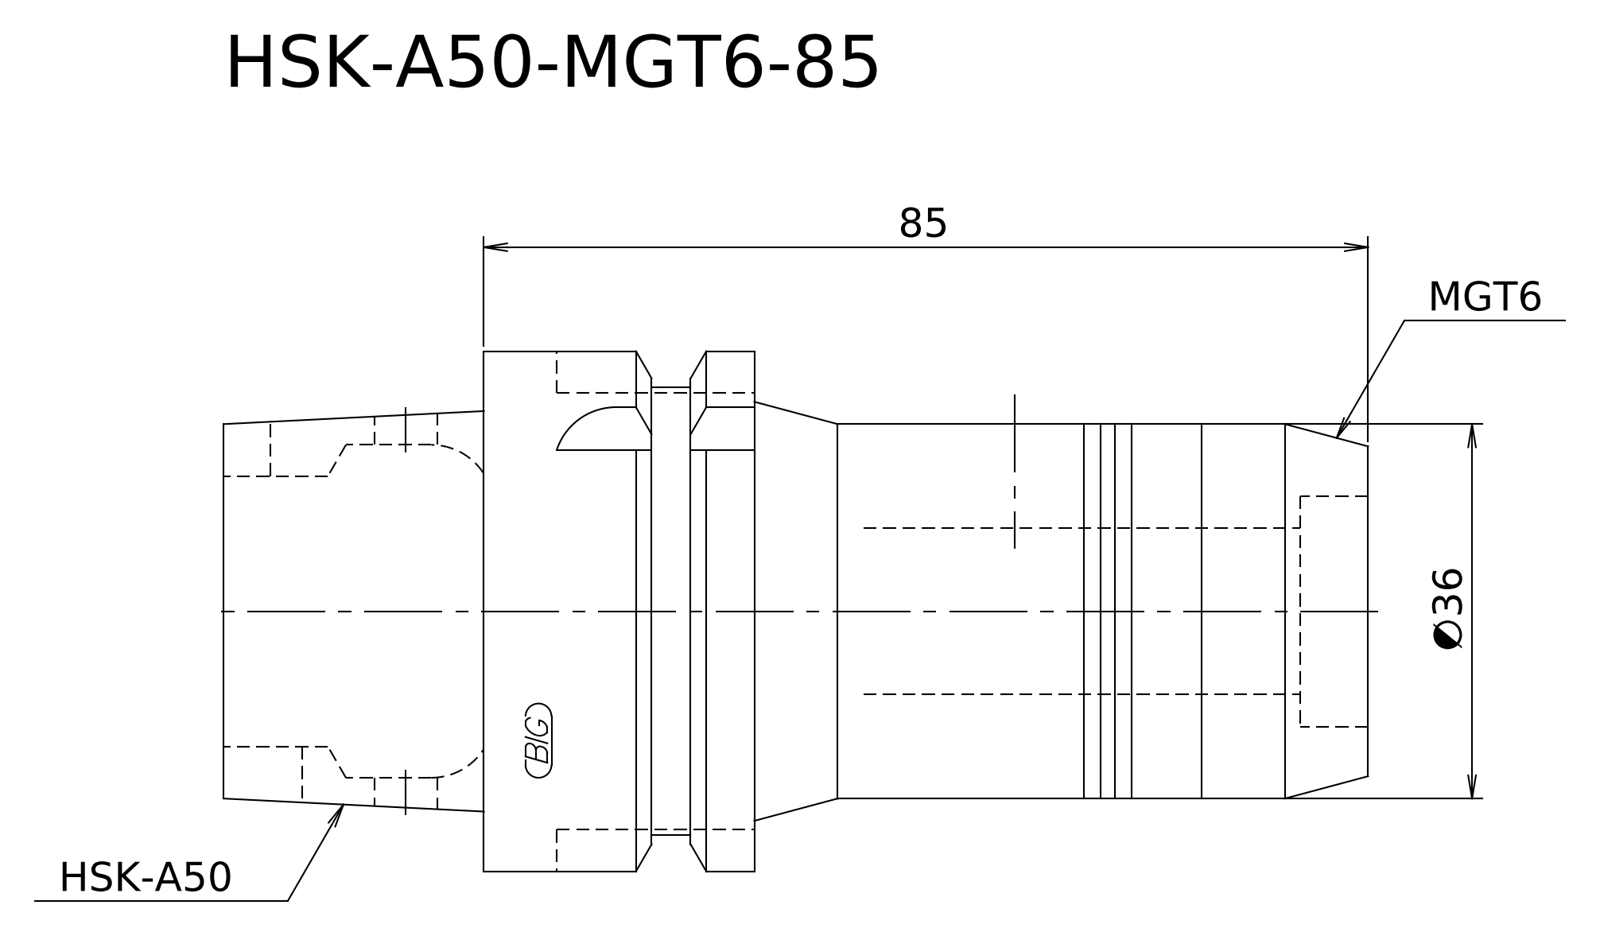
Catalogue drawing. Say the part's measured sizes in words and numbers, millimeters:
Its 3-D file was written by "Kubotek KeyCreator V8.5.1 (14335) (CONFIG_CONTROL_DESIGN)". It is 1 solid with 16 faces: 6 planar, 5 cylindrical and 5 other. Overall it measures 110 by 50 by 50 millimeters. Its volume is 135 915 cubic millimeters and its surface area 17 645 square millimeters. Round bosses or shafts: 1 of diameter 50, 1 of diameter 43, 1 of diameter 38.3, 1 of diameter 36. The main face-to-face distances are 25, 85, 110, 59, 26, 51, 65.12, 6.12, 19.88, 44.88.
